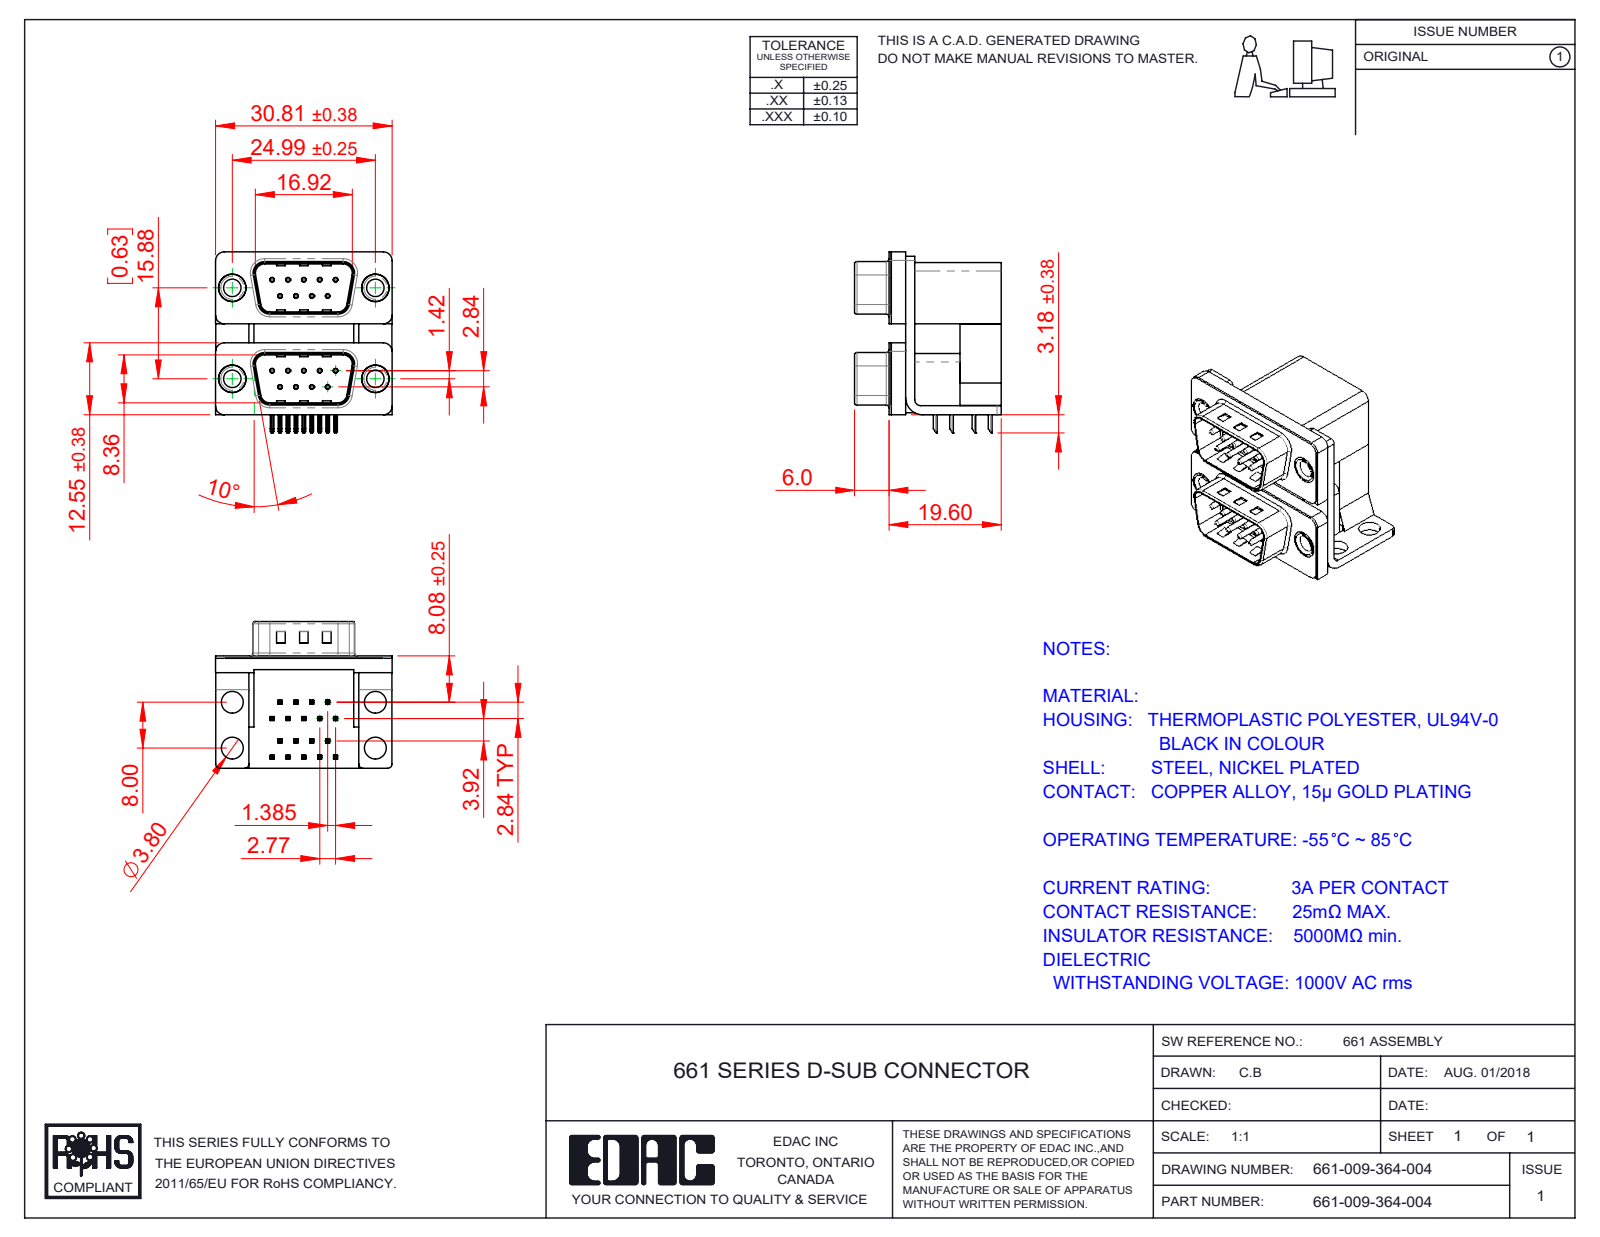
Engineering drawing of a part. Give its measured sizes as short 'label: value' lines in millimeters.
name: 661 Housing Upper_09 Contacts L; 661 Mounting Bracket_NoneL; 661 Shell_09 Contacts; 661 Contact Top Lower (+7 more)
written by: SolidWorks 2020 (CONFIG_CONTROL_DESIGN)
unit: mm
bodies: 29 solids, 1864 faces (1152 planar, 558 cylindrical, 154 other)
size: 31.61 × 30.81 × 25.6
volume: 9 790 mm³; area: 11 310 mm²
holes: 18× ⌀0.35, 18× ⌀0.8, 4× ⌀3.05, 4× ⌀3.5, 4× ⌀3.8, 4× ⌀4, 4× ⌀4.8, 4× ⌀5
bosses: 18× ⌀0.75, 4× ⌀4.9, 4× ⌀4.75, 4× ⌀3.85
rounds: 72× R0.25, 36× R0.12, 16× R0.5, 13× R1.5, 8× R0.75, 8× R0.9, 8× R1.6, 8× R2
face distances: 0.4, 2.5, 16.7, 19.2, 15.87, 1.6, 7.2, 9.5, 12, 19.6
hole spacings: 3.16, 16.12, 2.77, 15.88, 16.82, 18.77, 5.54, 5.04
